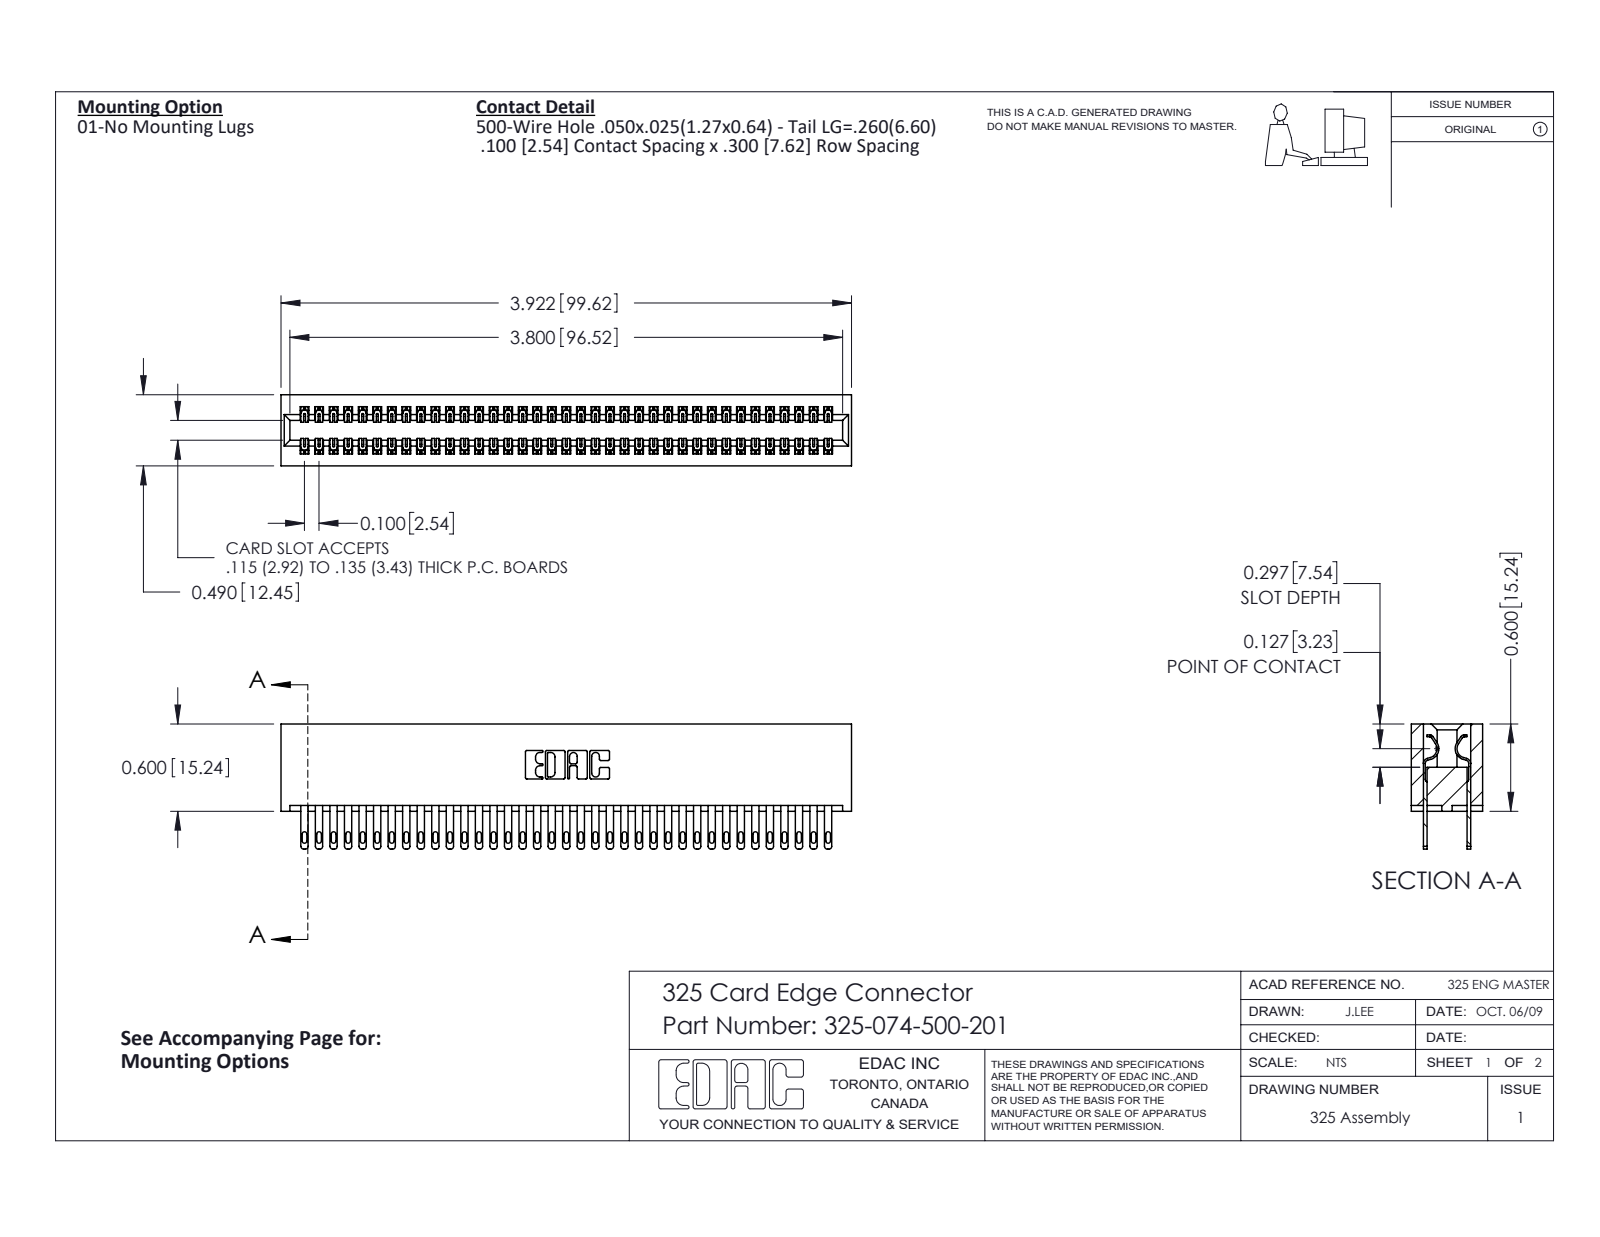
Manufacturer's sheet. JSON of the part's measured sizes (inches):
{"part_name": "325-074-500-201; 325-292-001_325-293-100; 325 Part_Lugless", "step_written_by": "SolidWorks 2016 (CONFIG_CONTROL_DESIGN)", "units": "inches", "bodies": {"solids": 75, "faces": 3658, "planar": 2286, "cylindrical": 1372, "other": 0}, "overall_size": [3.922, 0.86, 0.49], "volume_in3": 0.833, "surface_area_in2": 27.64, "partial_cylinders_radius": [[0.006, 111], [0.016, 74], [0.02, 74], [0.01, 22], [0.007, 6], [0.031, 6], [0.026, 3], [0.014, 2]], "face_to_face_distances": [0.083, 0.407, 0.3, 0.107, 0.383, 0.025, 0.325, 0.49, 0.275, 0.56]}
